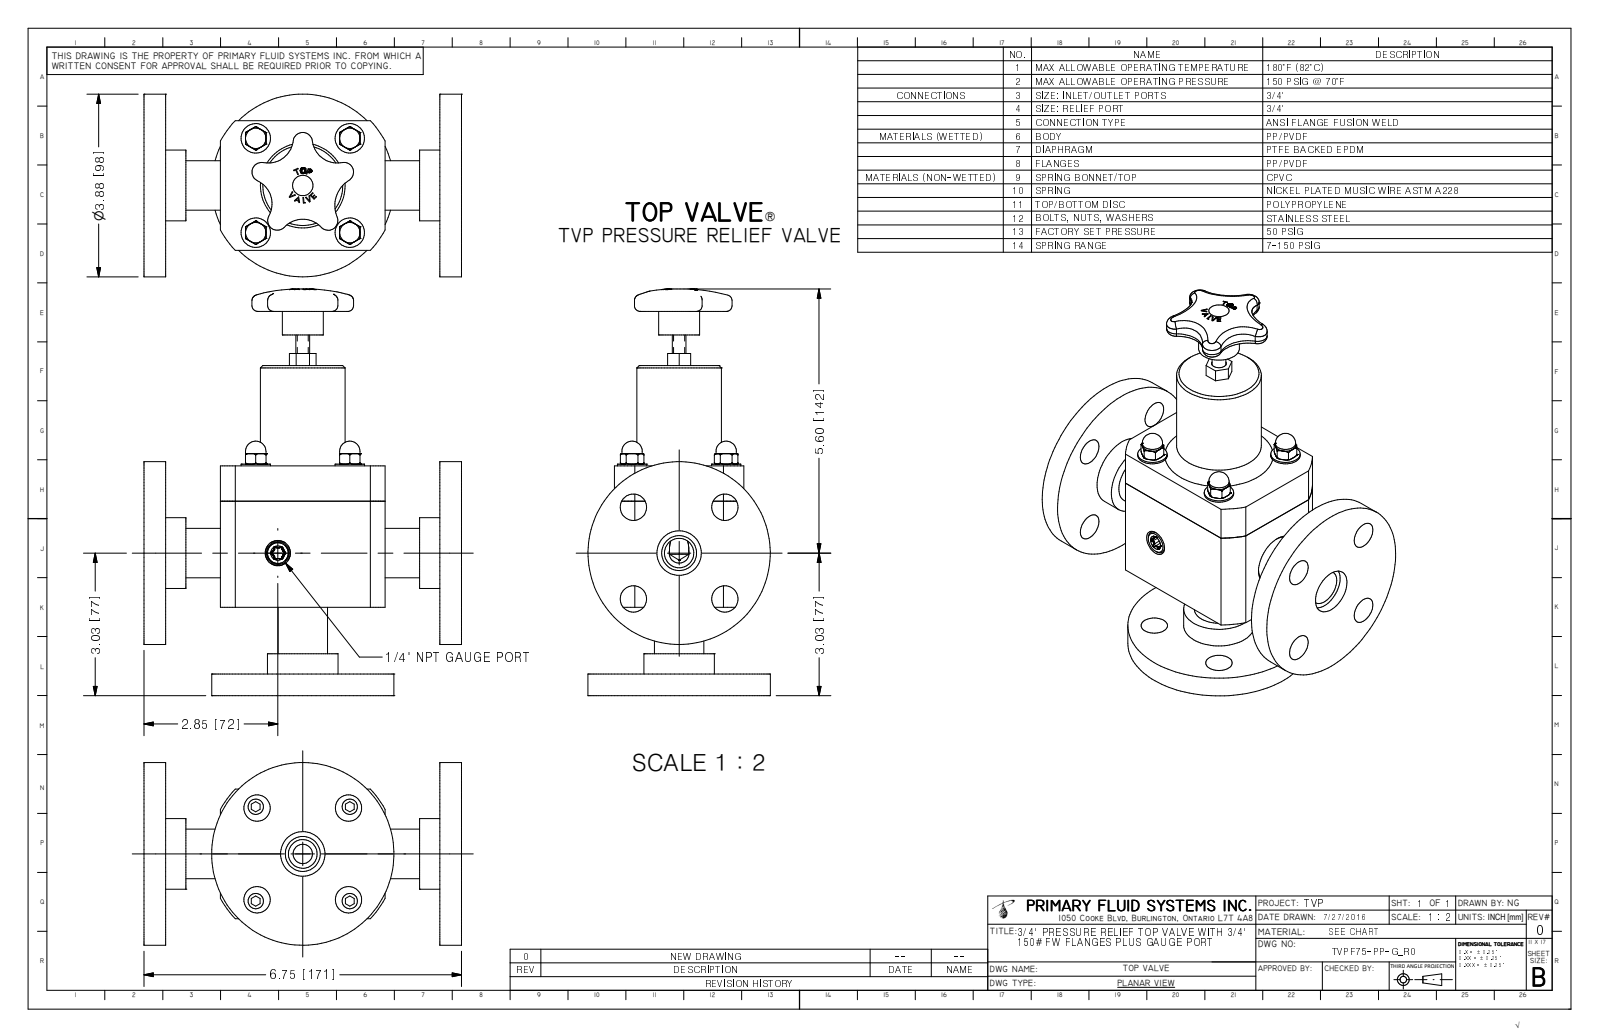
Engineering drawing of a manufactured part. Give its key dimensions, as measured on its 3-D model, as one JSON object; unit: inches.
{"part_name": "TVPF75-PP-G_R0", "step_written_by": "Autodesk Inventor 2009 (AUTOMOTIVE_DESIGN)", "units": "inches", "bodies": {"solids": 1, "faces": 362, "planar": 143, "cylindrical": 74, "other": 145}, "overall_size": [8.625, 6.75, 3.875], "volume_in3": 51.72, "surface_area_in2": 195.3, "round_holes": [[0.56, 8], [0.175, 4], [0.742, 2], [0.945, 2], [2.4, 1]], "round_bosses_or_shafts": [[0.625, 4], [0.433, 4], [3.875, 2], [1.5, 2], [1.05, 2], [2.375, 1], [1.8, 1], [0.87, 1]], "partial_cylinders_radius": [[0.027, 6], [0.085, 5], [0.205, 5], [0.536, 4], [0.656, 4], [0.625, 1], [0.745, 1], [1.988, 1]], "face_to_face_distances": [0.46, 6.29, 5.125, 6.75, 1.625, 1.165, 4.665, 5.83, 2.75, 1.875], "hole_center_spacings": [1.375, 1.945, 1.972, 0.039, 1.414, 2, 2.75, 2.789]}
